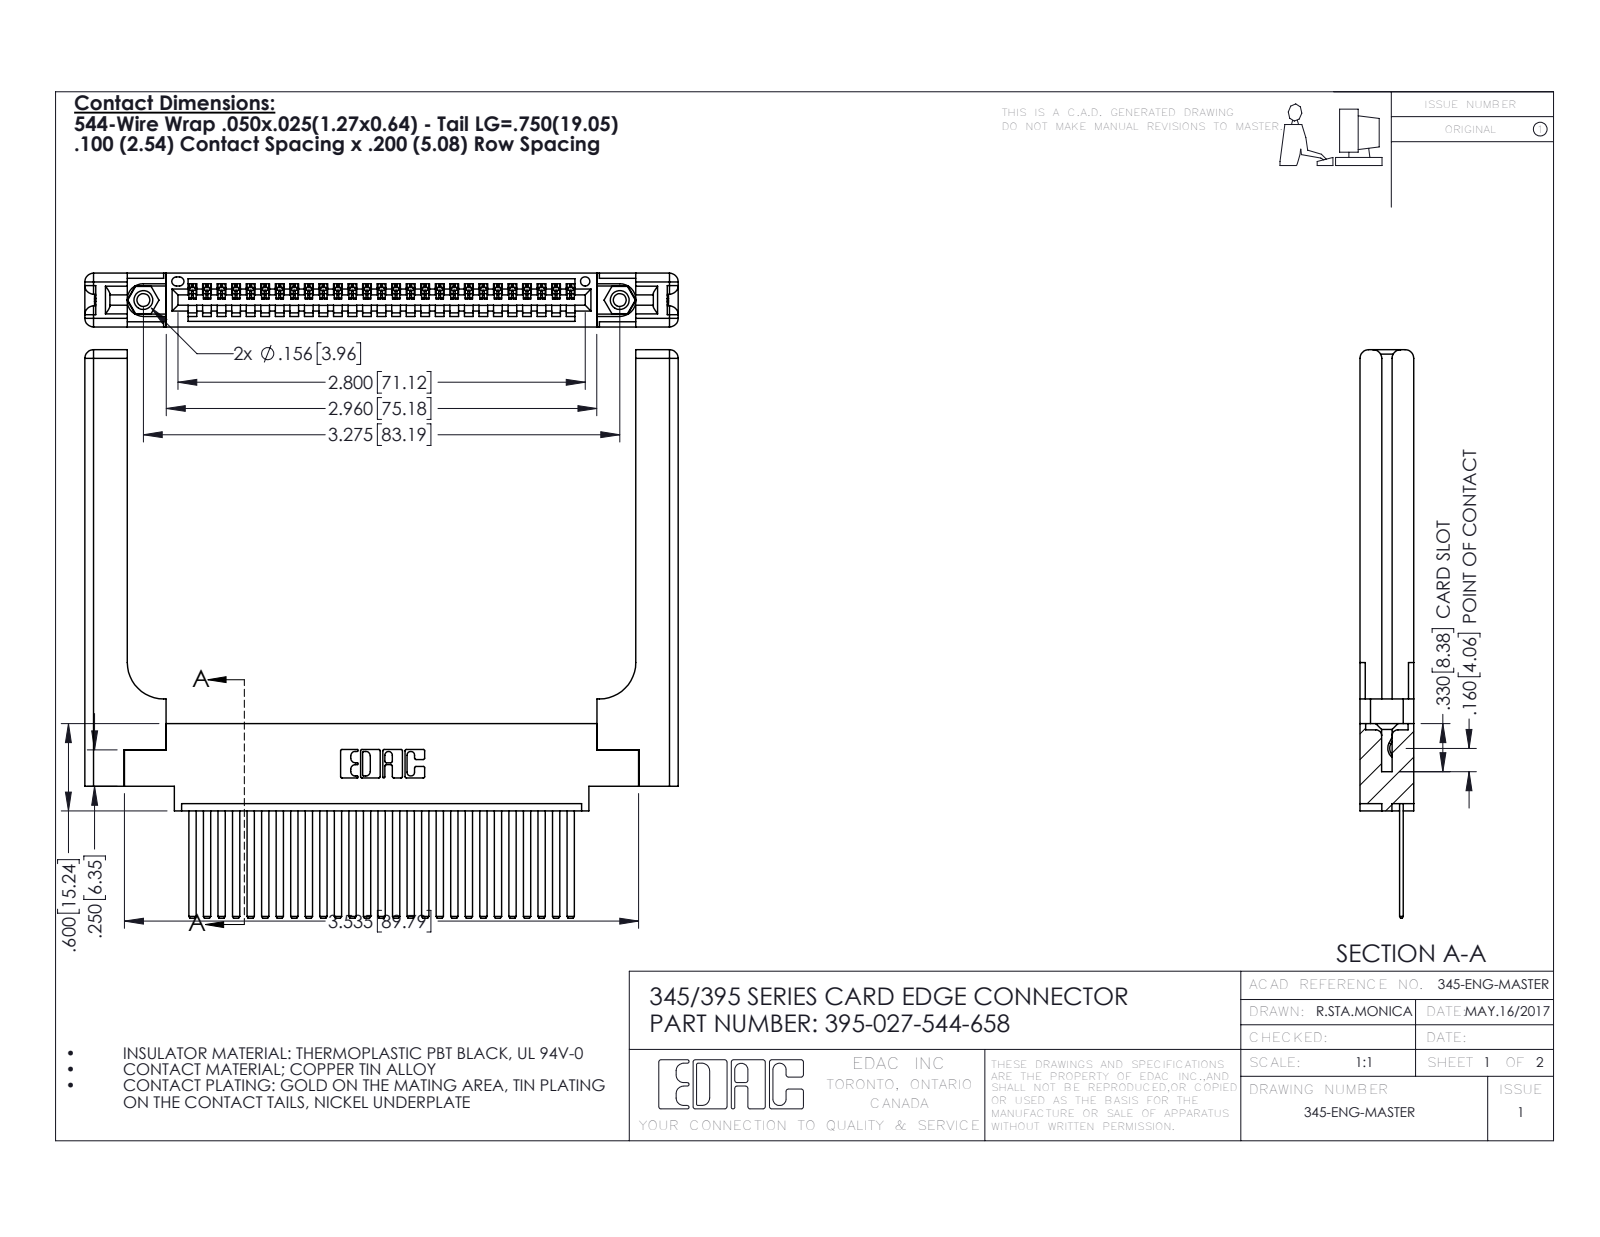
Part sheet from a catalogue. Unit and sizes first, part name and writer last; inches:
Units: inches
Overall size (bounding box): 4.079 × 3.907 × 0.37
Round holes (diameter × count): ⌀0.089 ×2, ⌀0.125 ×2, ⌀0.156 ×2, ⌀0.064 ×1
Round bosses / shafts (diameter × count): ⌀0.155 ×2
Partial cylindrical surfaces — rounded edges, fillets, slot ends (radius × count): R0.006 ×54, R0.01 ×22, R0.06 ×16, R0.007 ×6, R0.031 ×6, R0.026 ×3, R0.03 ×2, R0.031 ×2
Main face-to-face distances: 0.37, 0.072, 0.298, 0.098, 0.272, 0.025, 0.2, 0.148, 0.15, 0.077
Hole centre spacings: 0.27, 3.04, 3.275
Volume: 1.124 in³ · Surface area: 29.99 in²
Bodies: 32 solids, 1790 faces (1204 planar, 526 cylindrical, 60 other)
Part name (STEP PRODUCT): 345-250-001_345-250-001-102; 345-292-001_345-293-144; 345-220-058_345-220-058; 395-027-544-658 (+1 more)
STEP written by: SolidWorks 2016 (CONFIG_CONTROL_DESIGN)
